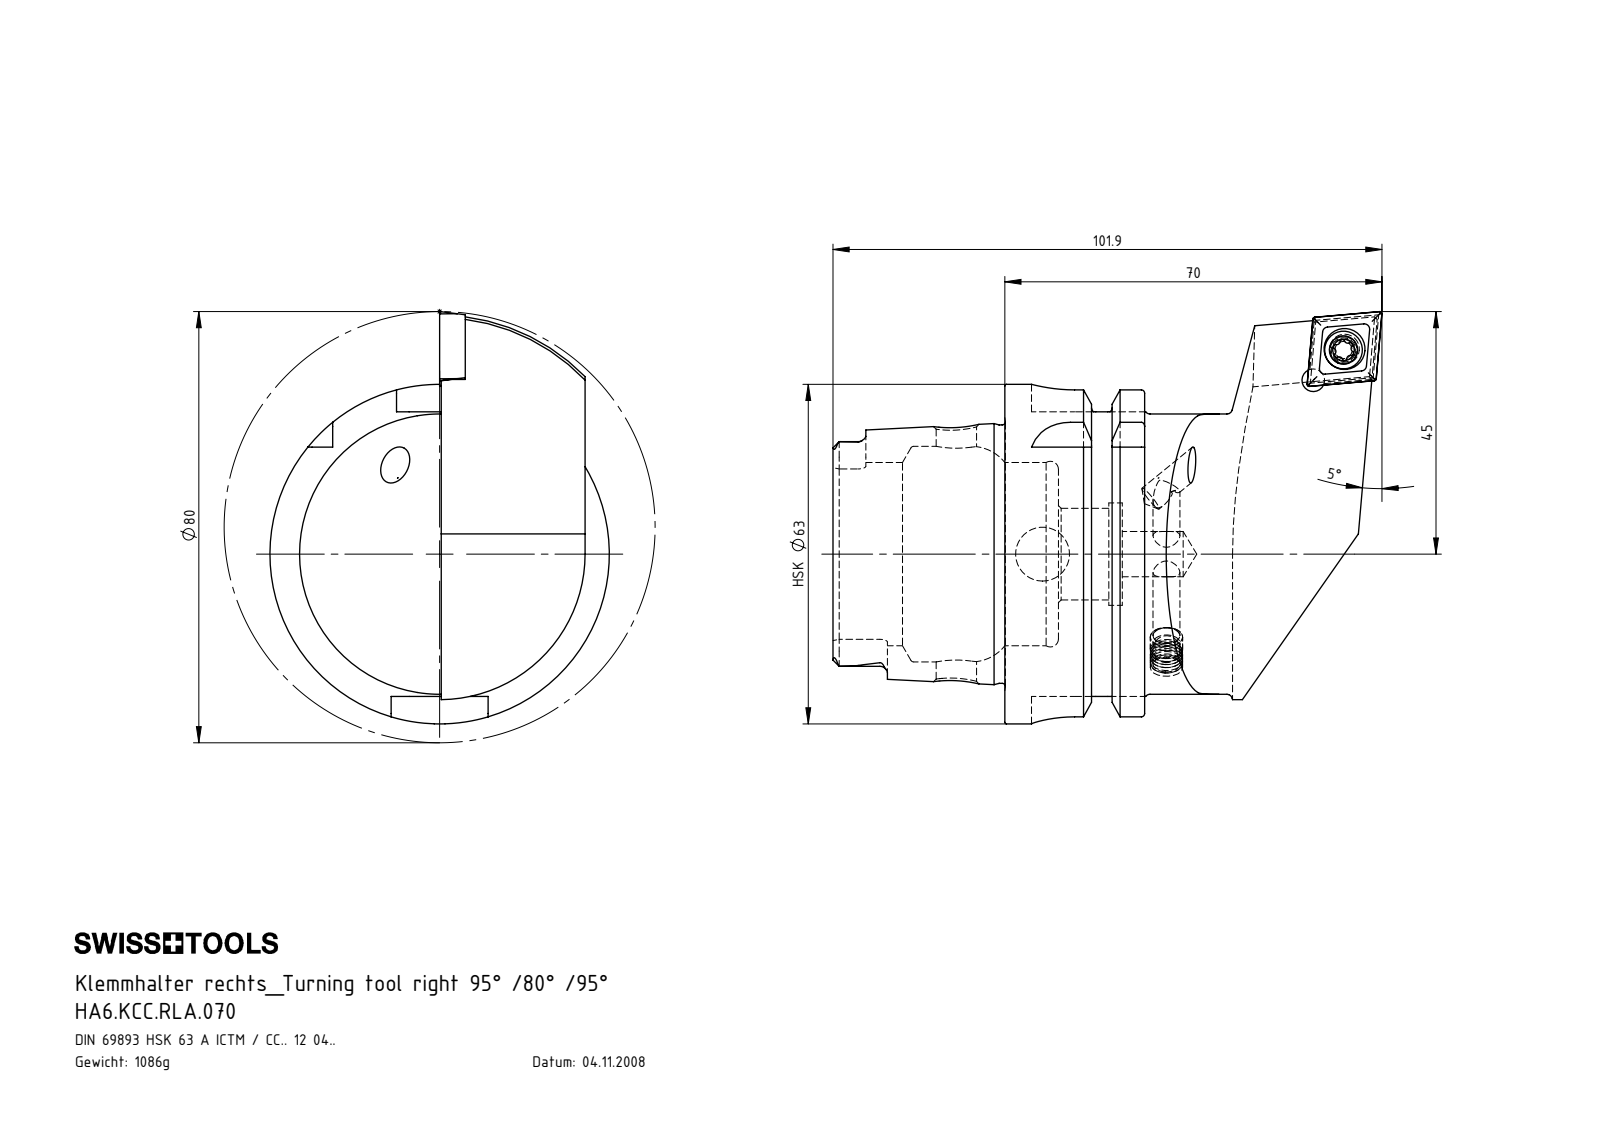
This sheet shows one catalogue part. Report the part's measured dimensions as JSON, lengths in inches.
{"part_name": "HA6-KCC.RLA.070; KVT_MB_600_050; CCMT120404; WCC-ER2.001.010_A (+1 more)", "step_written_by": "SolidWorks 2012 (CONFIG_CONTROL_DESIGN)", "units": "inches", "bodies": {"solids": 5, "faces": 308, "planar": 76, "cylindrical": 92, "other": 140}, "overall_size": [4.012, 3.012, 2.48], "volume_in3": 8.463, "surface_area_in2": 47.55, "round_holes": [[0.165, 4], [0.157, 1], [0.197, 1], [0.217, 1], [0.295, 1], [0.299, 1], [0.331, 1], [0.394, 1], [0.669, 1], [0.748, 1], [1.339, 1], [1.575, 1]], "round_bosses_or_shafts": [[0.197, 2], [2.48, 1], [2.163, 1], [2.047, 1], [1.887, 1], [0.276, 1]], "partial_cylinders_radius": [[0.015, 6], [0.055, 6], [0.315, 4], [0.027, 3], [0.027, 3], [0.111, 2], [0.113, 2], [0.236, 1]], "face_to_face_distances": [1.051, 1.022, 0.63, 0.392, 1.256, 1.648, 2.278, 2.079, 0.858, 0.467], "hole_center_spacings": [0.319, 0.323, 2.351, 2.663, 2.667]}
